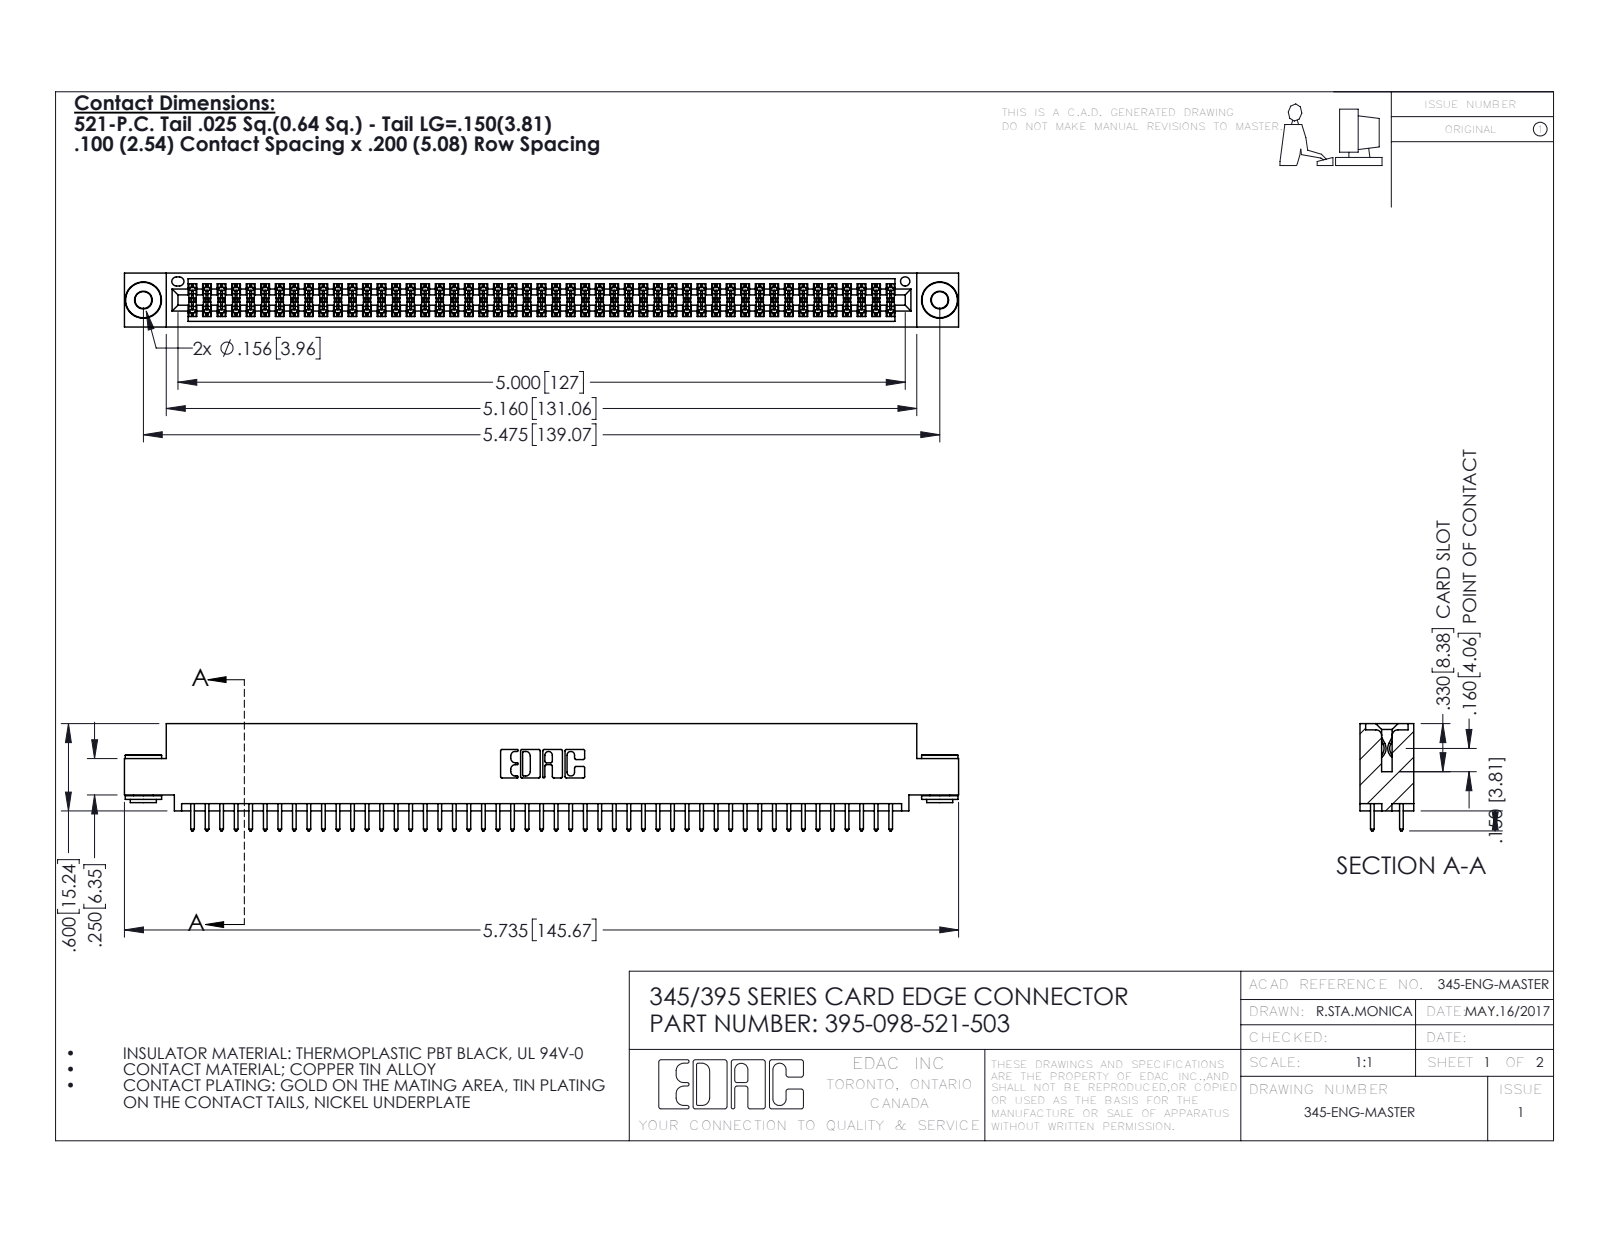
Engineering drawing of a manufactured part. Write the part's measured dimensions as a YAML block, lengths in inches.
part_name: "395-098-521-503; 345 Part_0.110 Offset - 0.156 Dia-TH; 345-250-002_345-250-002-102; 345-292-001_345-293-121"
step_written_by: "SolidWorks 2016 (CONFIG_CONTROL_DESIGN)"
units: inches
bodies: {solids: 101, faces: 5068, planar: 3328, cylindrical: 1732, other: 8}
overall_size: [5.735, 0.737, 0.37]
volume: 0.862
surface_area: 32.62
round_holes:
  - {diameter: 0.116, count: 2}
  - {diameter: 0.156, count: 2}
  - {diameter: 0.064, count: 1}
round_bosses_or_shafts:
  - {diameter: 0.25, count: 2}
  - {diameter: 0.18, count: 2}
  - {diameter: 0.136, count: 2}
partial_cylinders:
  - {radius: 0.006, count: 147}
  - {radius: 0.01, count: 98}
  - {radius: 0.01, count: 22}
  - {radius: 0.007, count: 6}
  - {radius: 0.031, count: 6}
  - {radius: 0.026, count: 3}
  - {radius: 0.014, count: 2}
  - {radius: 0.019, count: 2}
face_to_face_distances: [0.072, 0.298, 0.2, 0.025, 0.37, 0.098, 0.272, 0.225, 0.175, 0.149]
hole_center_spacings: [0.27, 5.239, 5.475]
